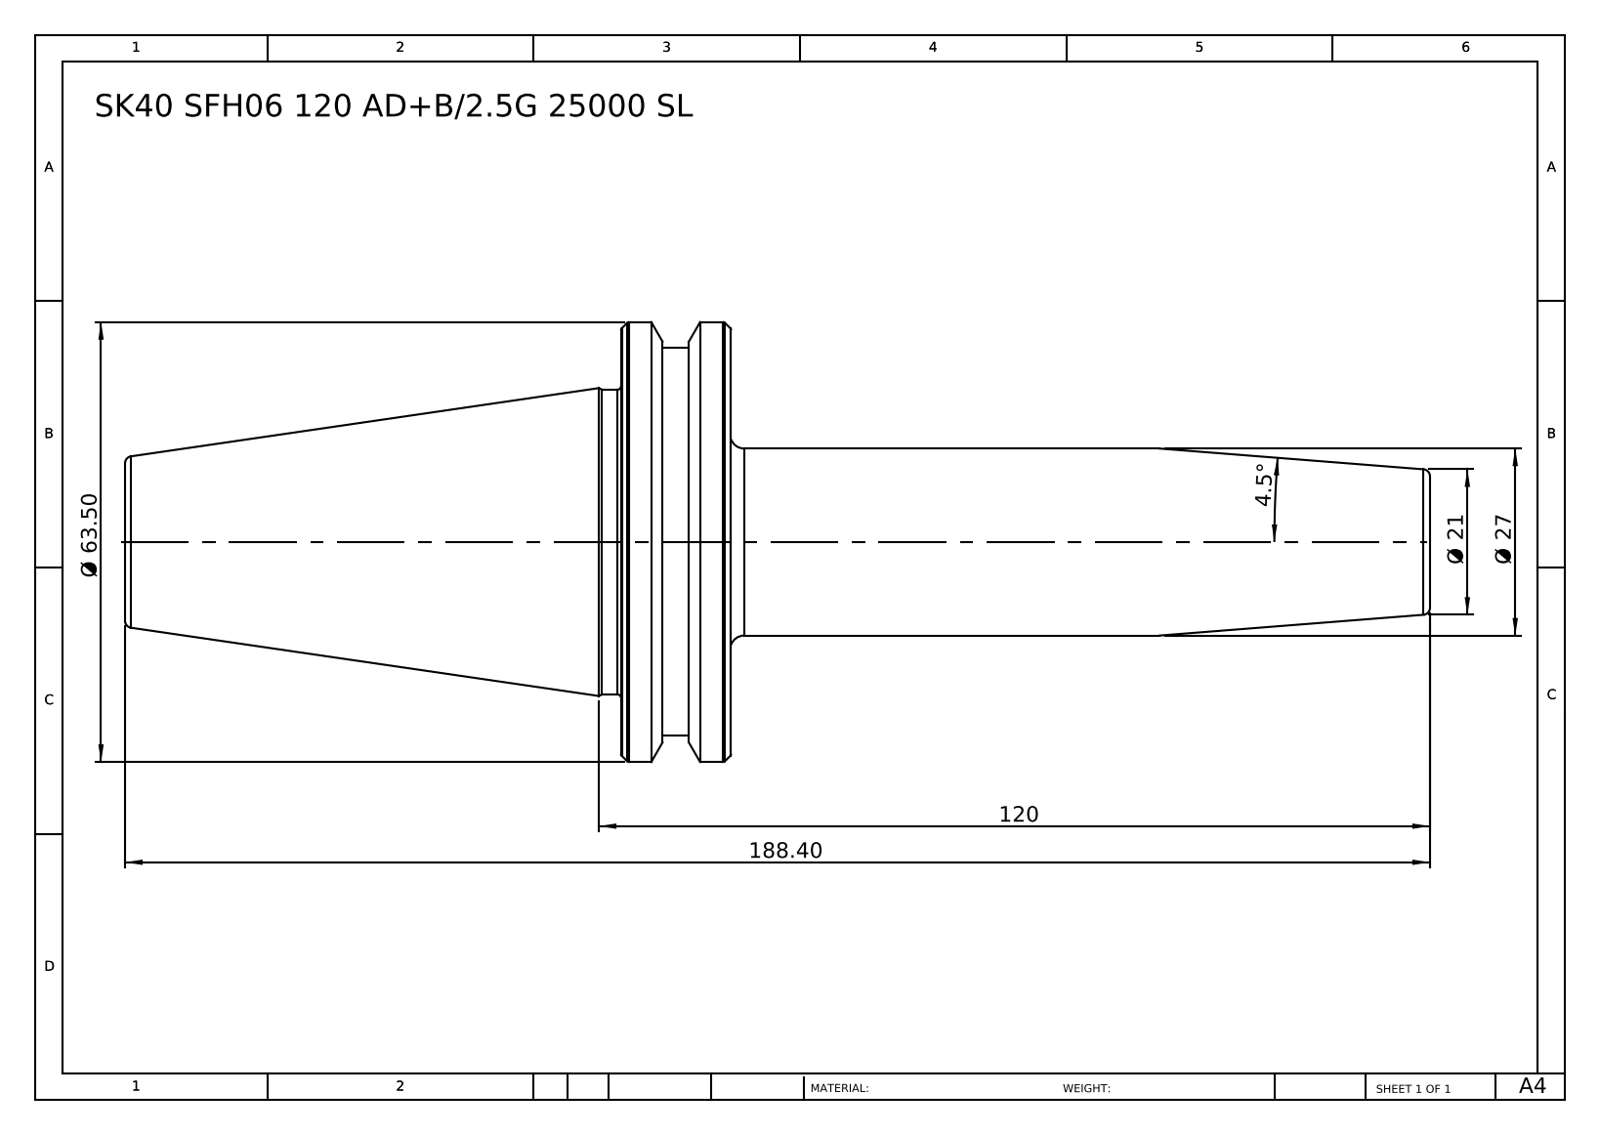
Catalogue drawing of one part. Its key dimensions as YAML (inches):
part_name: "SK40 SFH06 120 AD+B-2.5G 25000 SL"
step_written_by: "SolidWorks 2014 (CONFIG_CONTROL_DESIGN)"
units: inches
bodies: {solids: 1, faces: 46, planar: 6, cylindrical: 10, other: 30}
overall_size: [7.417, 2.5, 2.5]
volume: 10.39
surface_area: 38.44
round_bosses_or_shafts:
  - {diameter: 2.5, count: 1}
  - {diameter: 2.205, count: 1}
  - {diameter: 1.732, count: 1}
  - {diameter: 1.063, count: 1}
face_to_face_distances: [0.626, 3.445, 2.819, 3.972, 4.598, 7.417, 4.213, 0.24, 0.386, 3.205]
